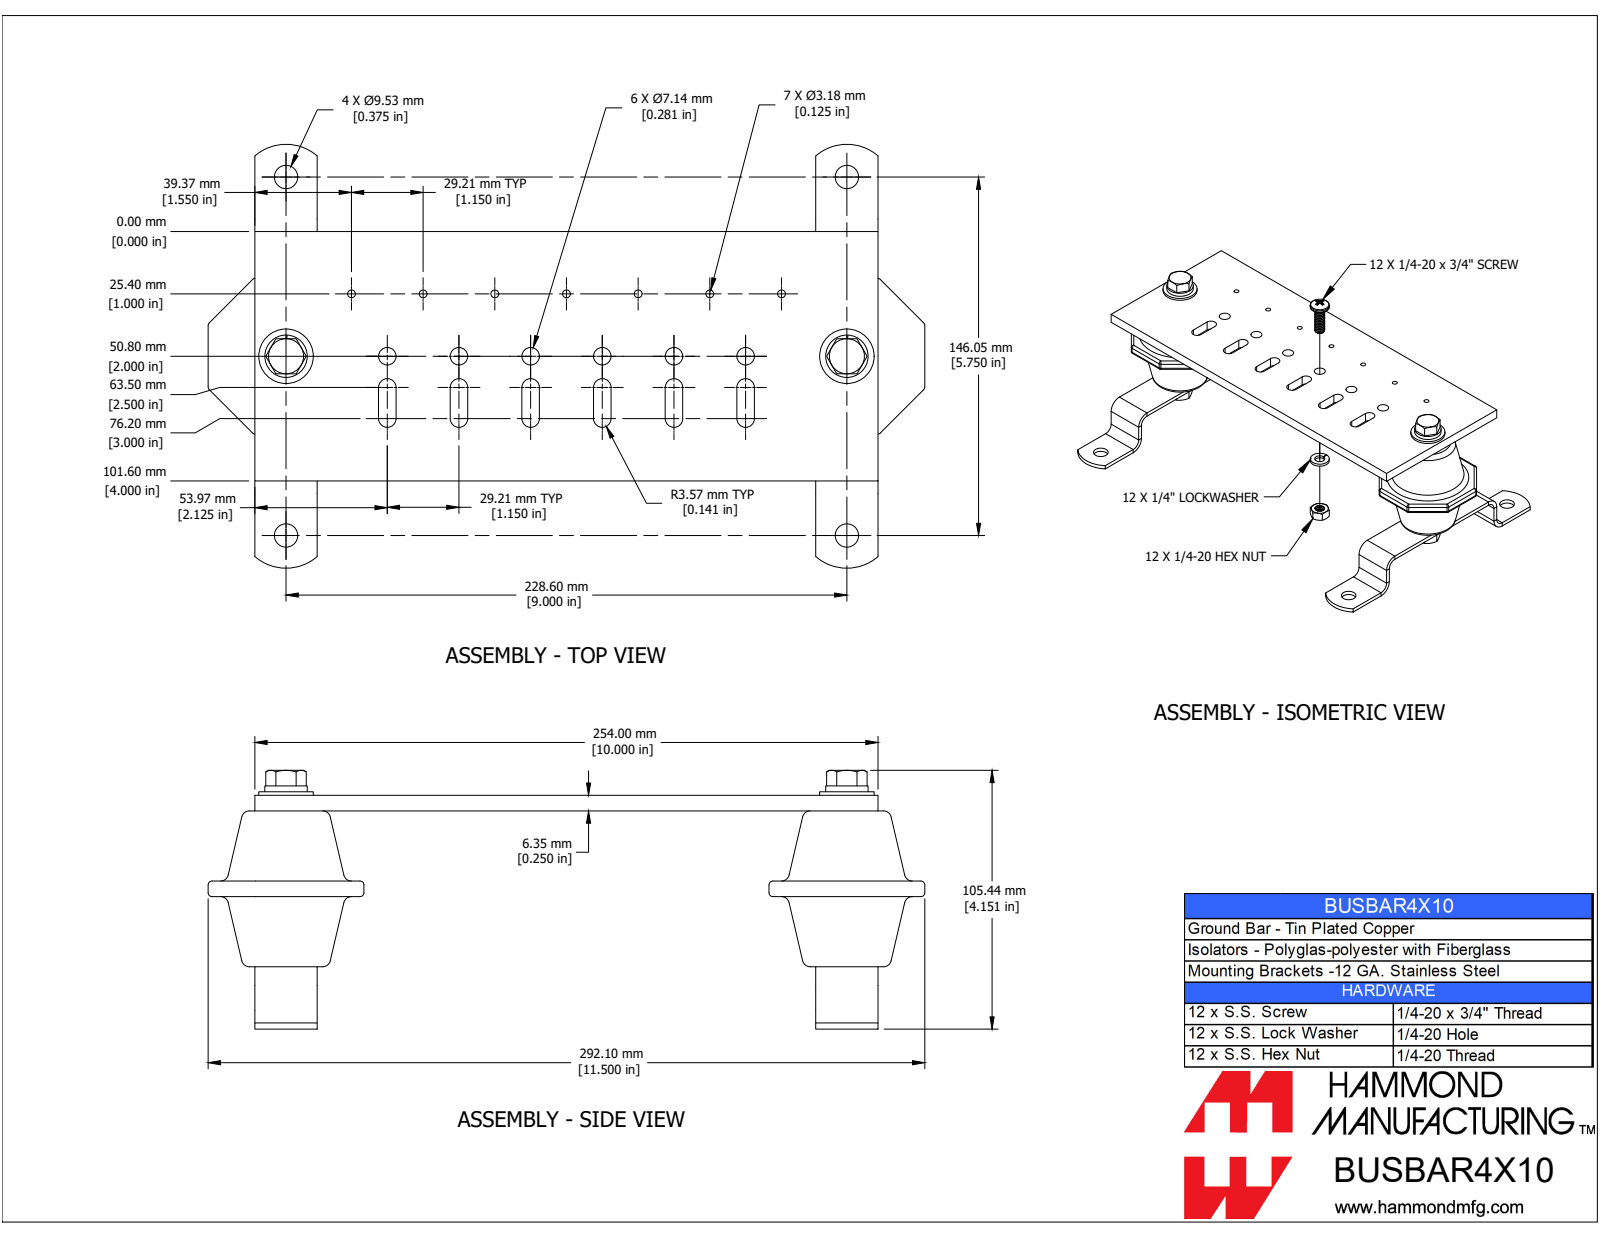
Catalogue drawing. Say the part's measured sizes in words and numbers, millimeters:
The part is named "BUSBAR4X10". Its 3-D file was written by "SolidWorks 2019 (AUTOMOTIVE_DESIGN)". It is 5 solids with 355 faces: 146 planar, 133 cylindrical and 76 other. Overall it measures 292.1 by 172.7 by 105.4 millimeters. Its volume is 387 700 cubic millimeters and its surface area 116 800 square millimeters. Round holes: 7 of diameter 3.2, 6 of diameter 7.1, 4 of diameter 9.5, 2 of diameter 7.8, 2 of diameter 10.3, 2 of diameter 12.7, 2 of diameter 14.3, 1 of diameter 9.8, 1 of diameter 9.8. Round bosses or shafts: 2 of diameter 22.2, 2 of diameter 17.3, 2 of diameter 9.5. Partial cylindrical surfaces (rounded edges, fillets, slot ends): 32 of radius 1.6, 13 of radius 1.6, 12 of radius 3.6, 4 of radius 5.1, 4 of radius 7.6, 4 of radius 19.3. The main face-to-face distances are 6.4, 2.5, 22.9, 25.4, 69.9, 63.5, 66, 72.4, 34.9, 88.9. The hole center spacings are 29.3, 29.2, 58.4, 87.6, 50.6, 50.6, 116.8, 146.1.
